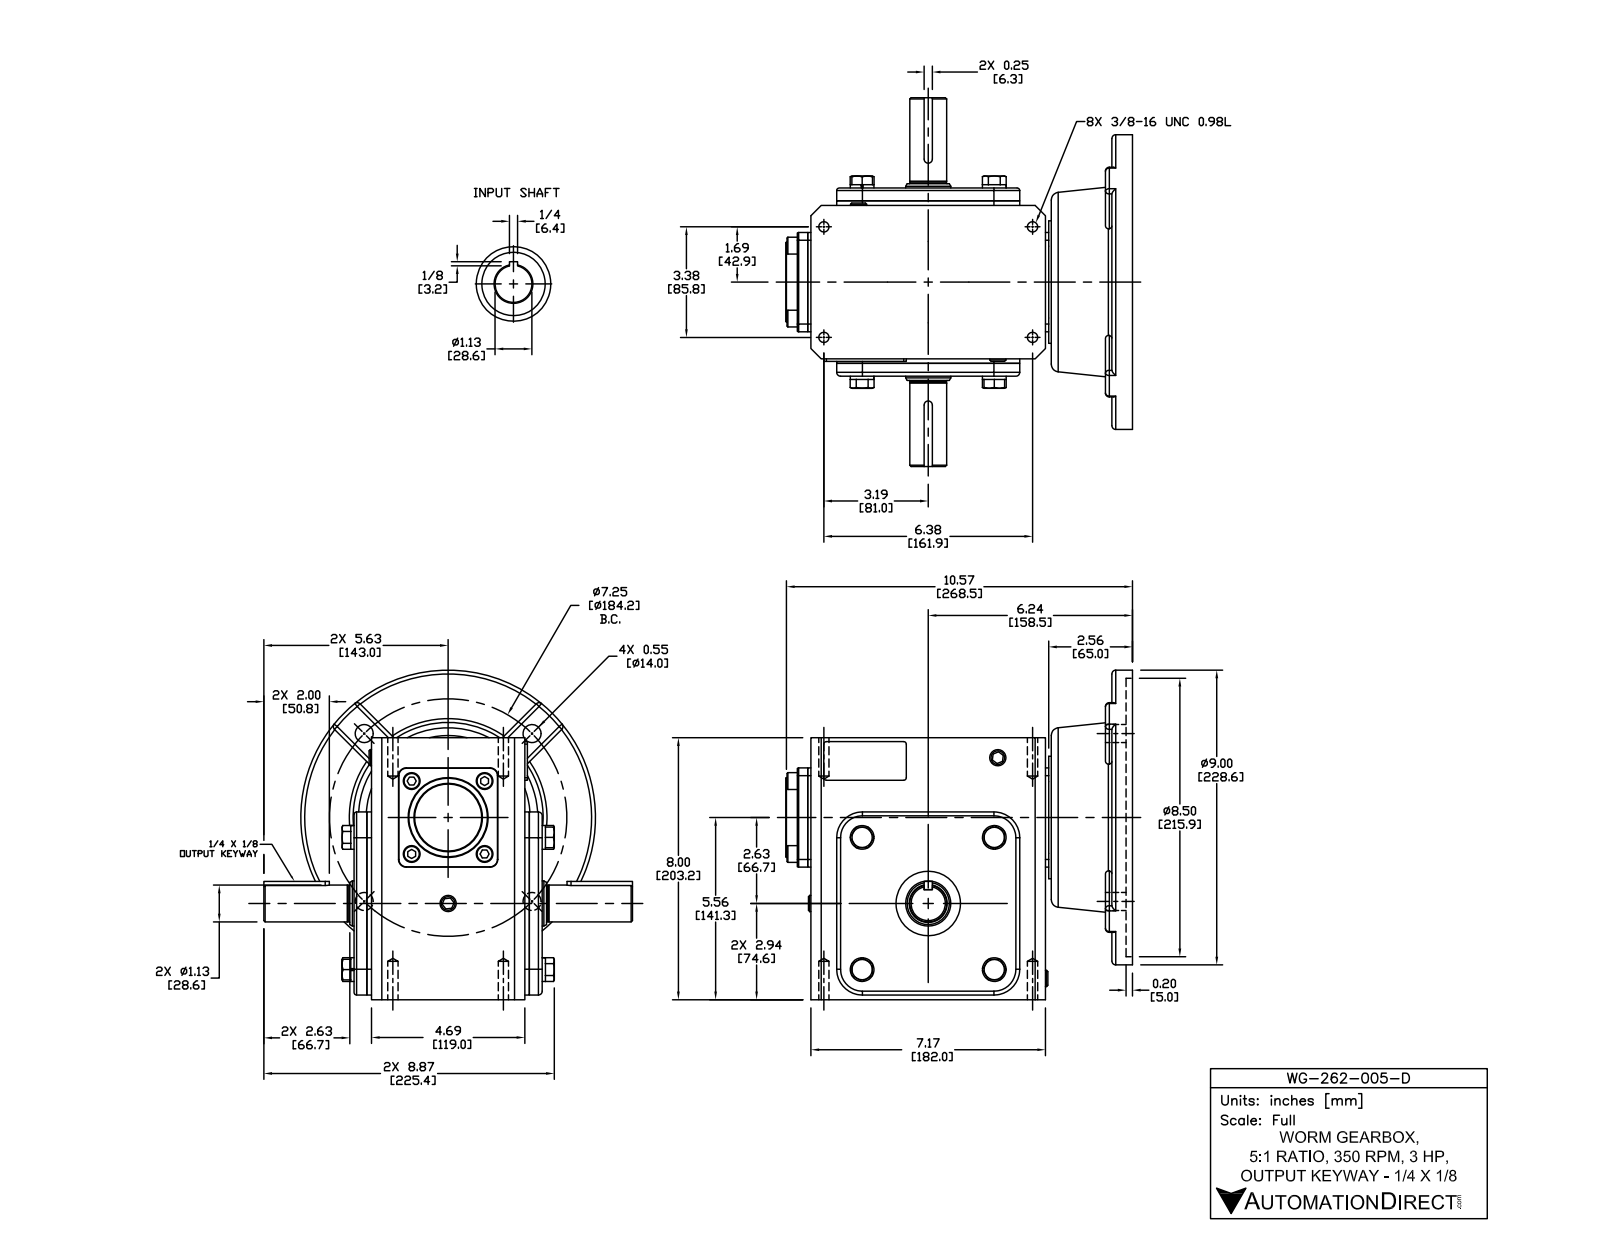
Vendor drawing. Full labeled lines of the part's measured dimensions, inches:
Part name (STEP PRODUCT): WG-262-005-D
STEP written by: SolidWorks 2015 (CONFIG_CONTROL_DESIGN)
Units: inches
Bodies: 32 solids, 579 faces (306 planar, 148 cylindrical, 125 other)
Overall size (bounding box): 11.26 × 10.591 × 10.063
Volume: 333.4 in³ · Surface area: 767.9 in²
Round holes (diameter × count): ⌀0.313 ×4, ⌀0.551 ×4, ⌀0.591 ×1, ⌀1.125 ×1, ⌀1.378 ×1, ⌀1.969 ×1, ⌀2.047 ×1, ⌀3.819 ×1, ⌀8.5 ×1
Round bosses / shafts (diameter × count): ⌀0.724 ×4, ⌀0.512 ×4, ⌀9 ×1, ⌀2.441 ×1, ⌀1.772 ×1, ⌀1.142 ×1, ⌀1.125 ×1, ⌀1.113 ×1
Partial cylindrical surfaces — rounded edges, fillets, slot ends (radius × count): R0.118 ×19, R0.079 ×7, R0.236 ×4, R0.787 ×4, R0.02 ×2, R0.039 ×2, R0.125 ×2
Main face-to-face distances: 4.961, 0.394, 5.354, 0.531, 5.217, 0.138, 4.823, 8, 0.433, 5.748
Hole centre spacings: 3.625, 5.127, 2.564, 3.375, 5.787, 6.375, 7.213, 7.25
